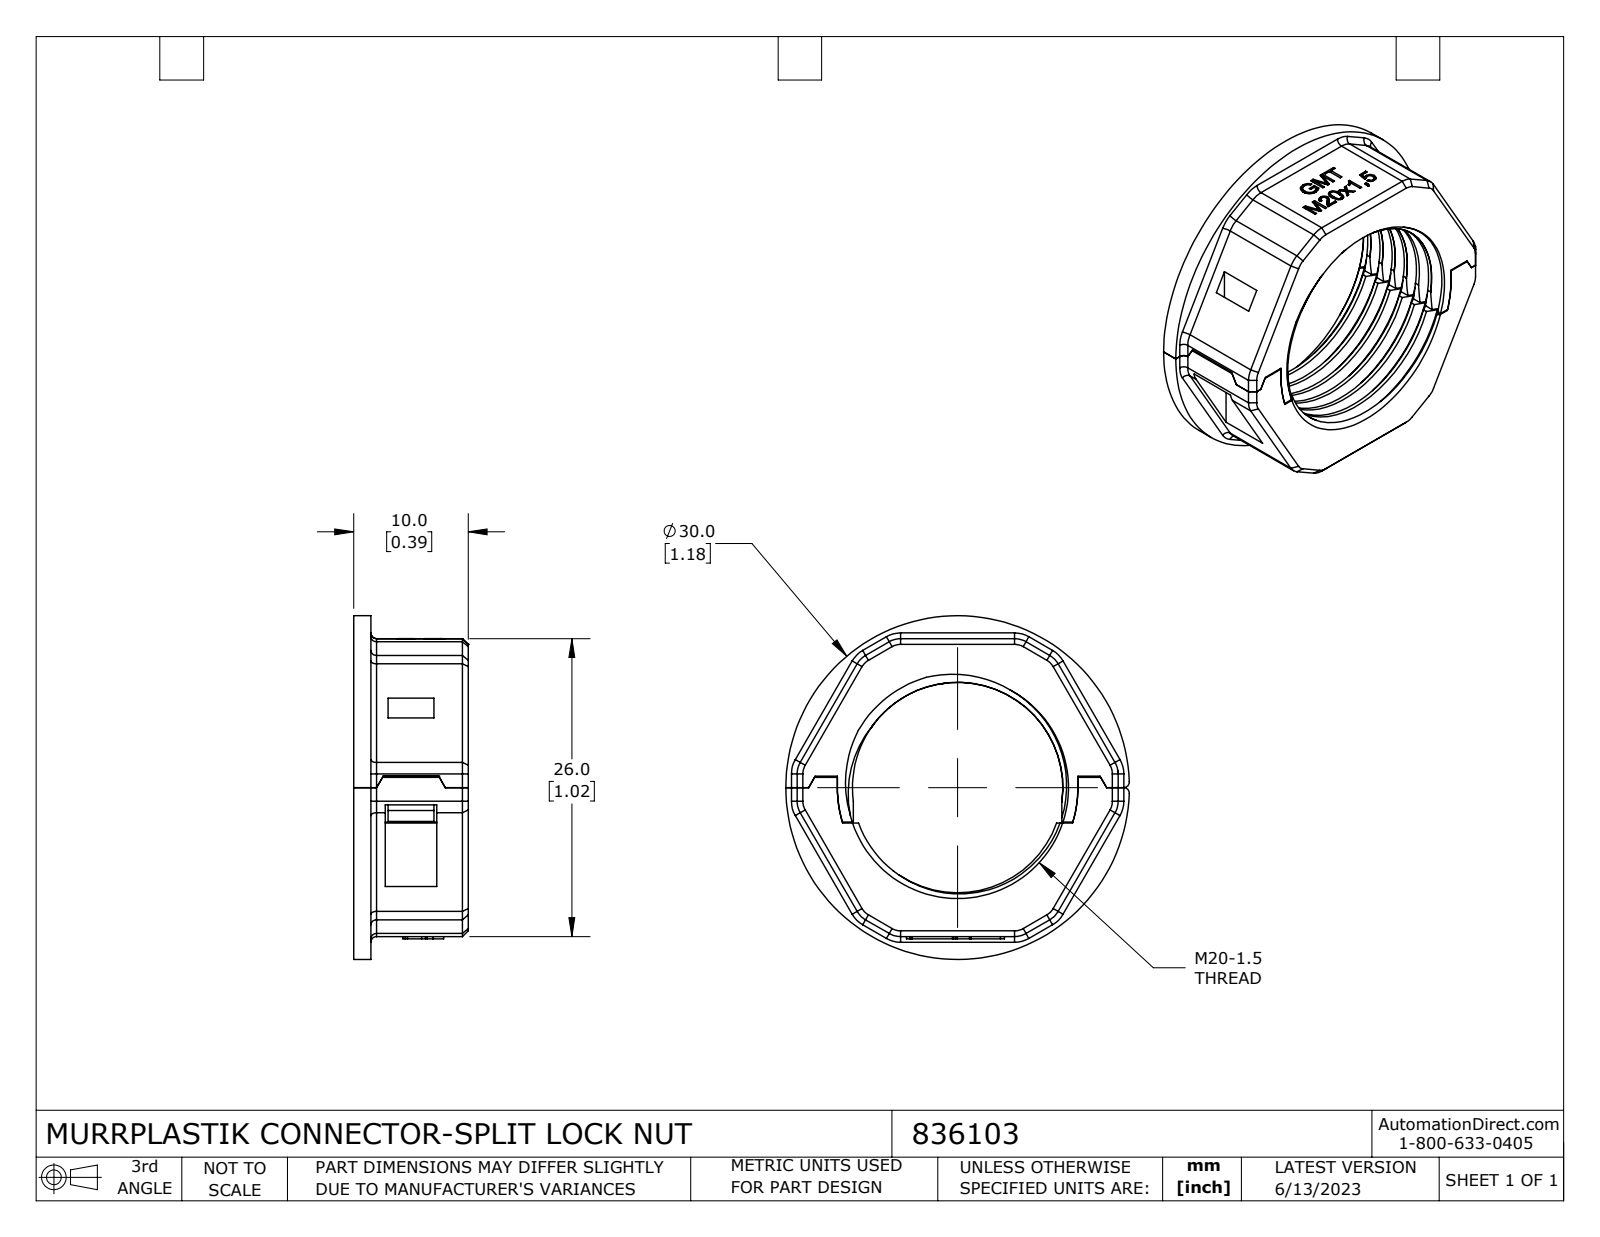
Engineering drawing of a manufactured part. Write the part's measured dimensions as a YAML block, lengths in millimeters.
part_name: "836103"
step_written_by: "SolidWorks 2021 (CONFIG_CONTROL_DESIGN)"
units: millimeters
bodies: {solids: 2, faces: 439, planar: 220, cylindrical: 83, other: 136}
overall_size: [30, 30, 10]
volume: 2880
surface_area: 3154
round_holes:
  - {diameter: 6, count: 1}
  - {diameter: 18.4, count: 1}
  - {diameter: 20, count: 1}
round_bosses_or_shafts:
  - {diameter: 30, count: 1}
partial_cylinders:
  - {radius: 0.5, count: 14}
  - {radius: 2, count: 12}
  - {radius: 0.1, count: 2}
  - {radius: 10.5, count: 1}
face_to_face_distances: [10, 26, 1.5, 8.5, 3, 11.5, 1, 21, 2.7, 7.2]
